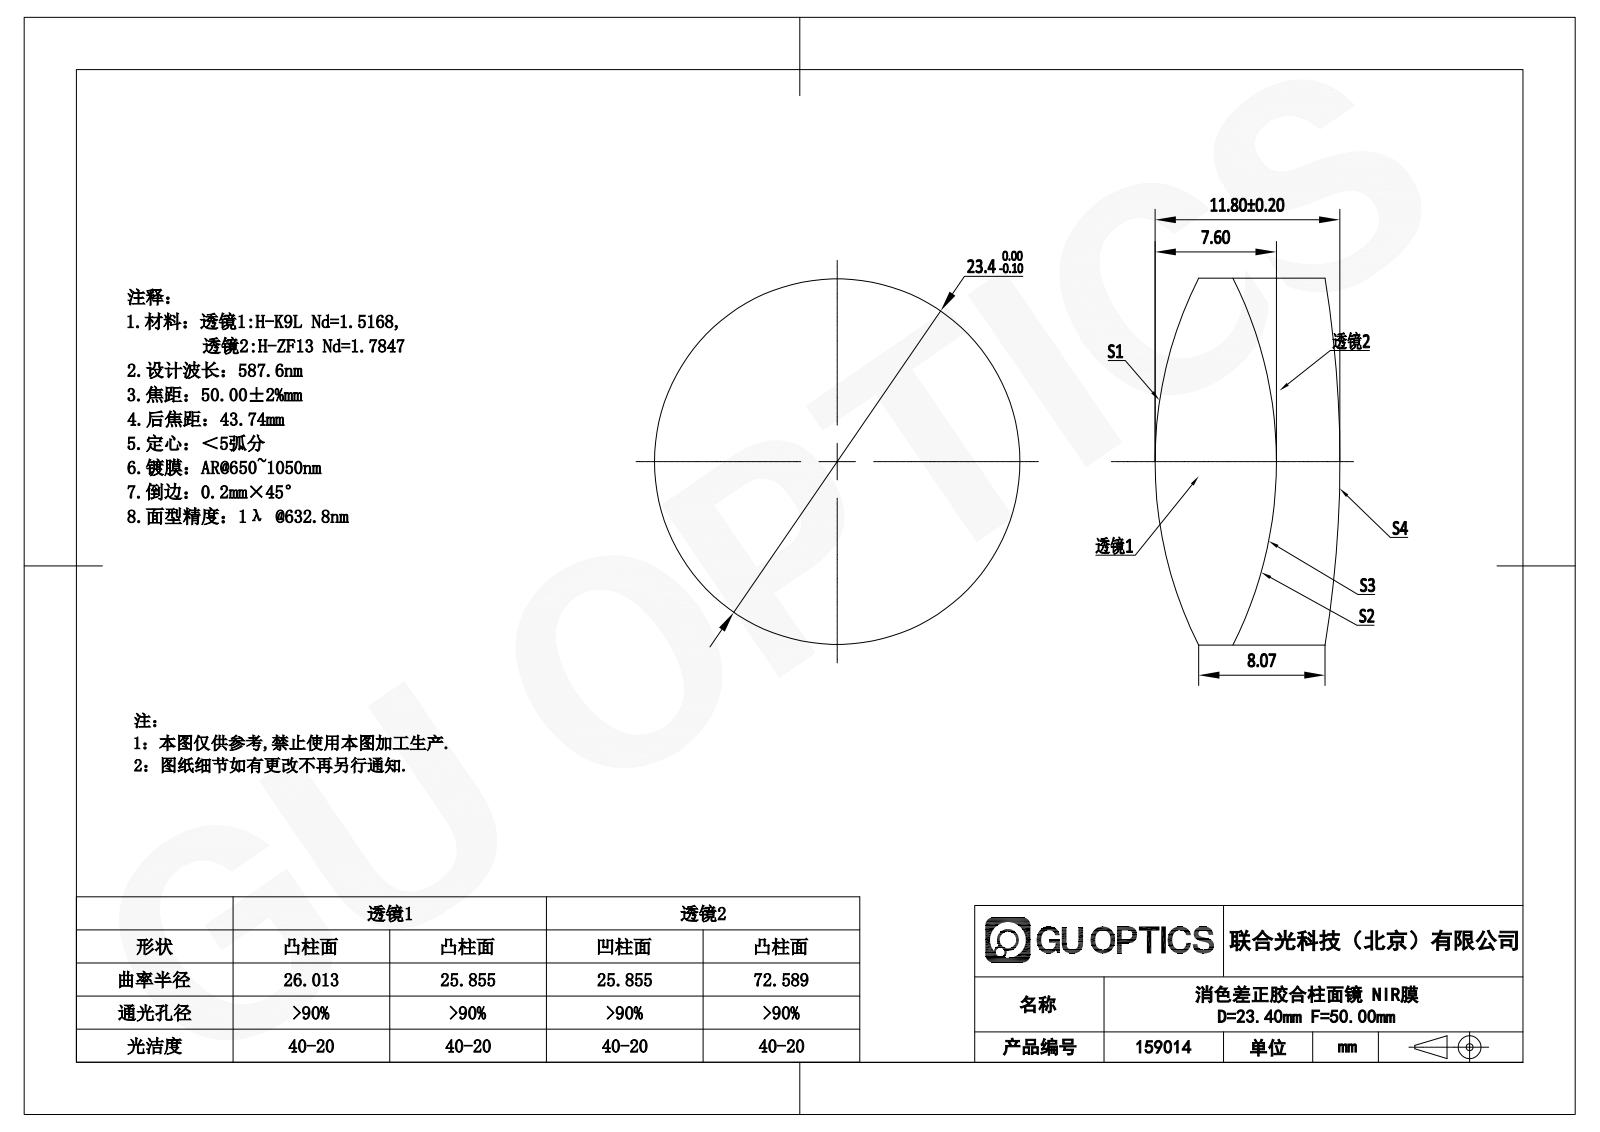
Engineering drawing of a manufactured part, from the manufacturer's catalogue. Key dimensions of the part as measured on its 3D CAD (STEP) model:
Part name (STEP PRODUCT): 159014
STEP written by: SolidWorks 2020 (CONFIG_CONTROL_DESIGN)
Units: millimetres
Bodies: 1 solid, 5 faces (0 planar, 5 cylindrical, 0 other)
Overall size (bounding box): 23.4 × 23.4 × 11.8
Volume: 4 682 mm³ · Surface area: 1 605 mm²
Round bosses / shafts (diameter × count): ⌀23.4 ×1
Partial cylindrical surfaces — rounded edges, fillets, slot ends (radius × count): R26.01 ×1, R72.59 ×1
